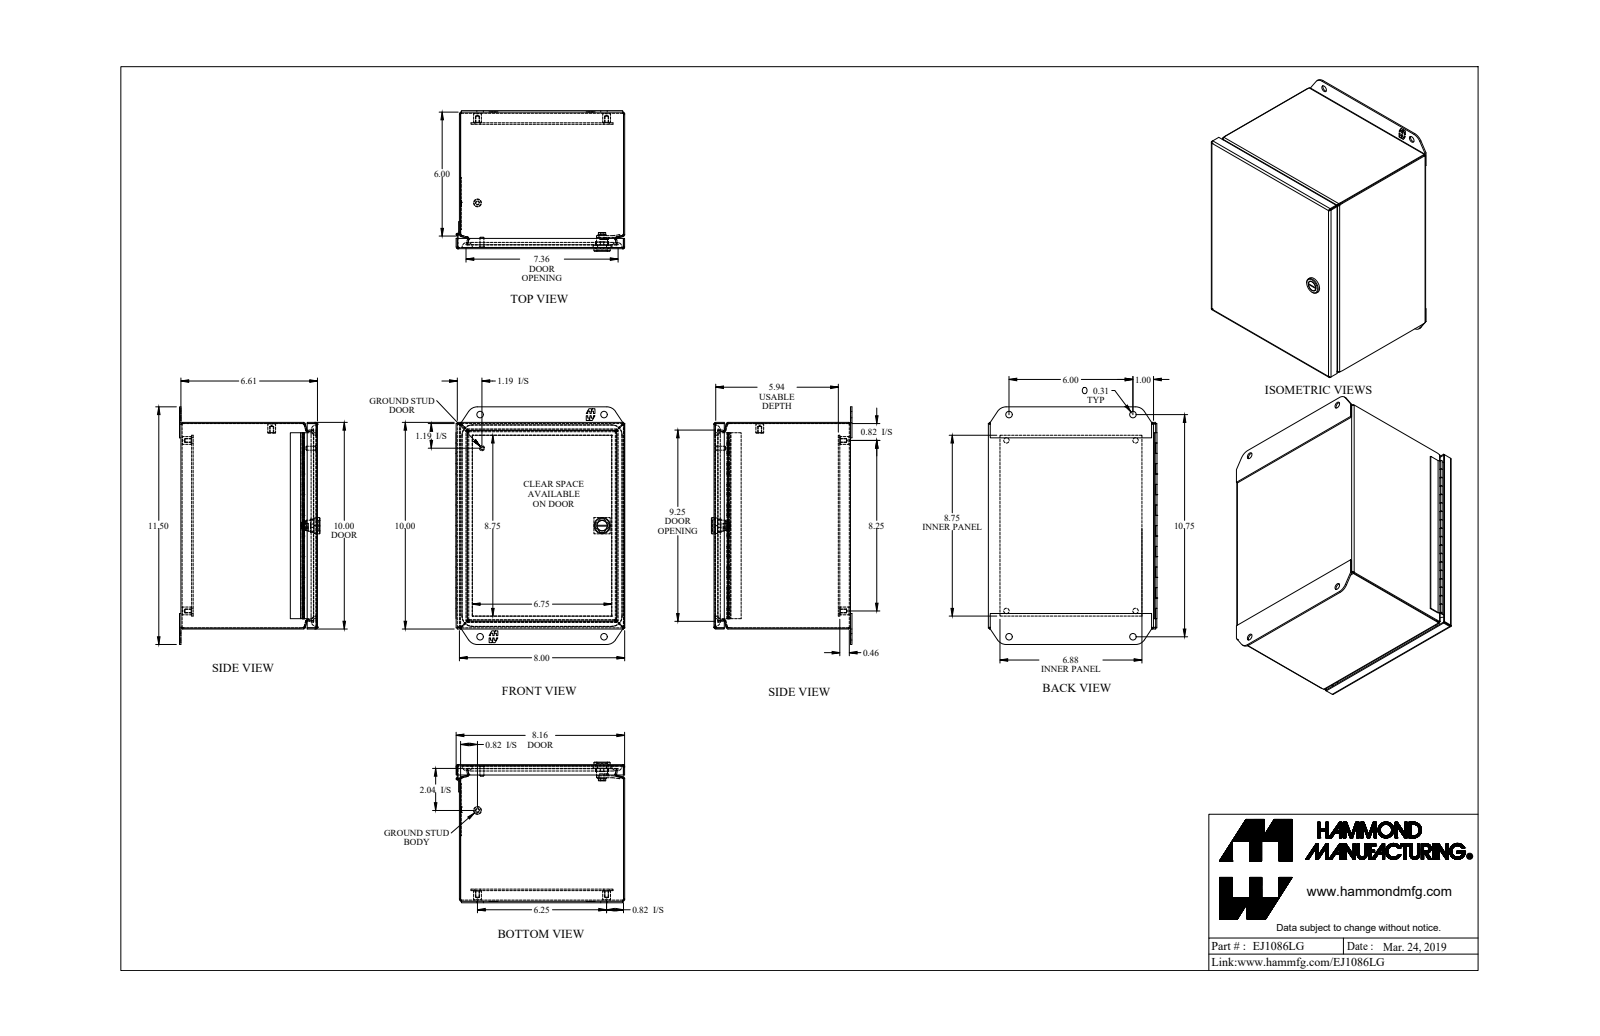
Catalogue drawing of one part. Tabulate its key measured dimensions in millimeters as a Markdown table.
| quantity | value |
| --- | --- |
| part name | EJ1086LG_Default |
| STEP written by | SolidWorks 2019 (CONFIG_CONTROL_DESIGN) |
| units | millimeters |
| bodies | 16 solids, 675 faces (377 planar, 206 cylindrical, 92 other) |
| overall size | 292.1 × 207.4 × 172.8 |
| volume | 548 300 mm³ |
| surface area | 716 100 mm² |
| round holes (diameter × count) | 4 × 5, 6.7 × 4, 8 × 4, 1.3 × 1, 13.1 × 1 |
| round bosses / shafts (diameter × count) | 9.5 × 5, 20 × 1, 13.6 × 1, 12.6 × 1, 11 × 1, 6.4 × 1, 4.8 × 1, 2.5 × 1 |
| partial cylindrical surfaces (radius × count) | 0.7 × 16, 2.2 × 16, 7.1 × 10, 6.4 × 4, 12.7 × 4, 12.7 × 4, 1.5 × 2, 13.7 × 2 |
| main face-to-face distances | 1.4, 166.5, 201.8, 252.6, 1.8, 15, 167.9, 165, 11.7, 13.1 |
| hole center spacings | 31.9, 31.9, 104.9, 152.4, 158.8, 158.8, 158.8, 185.6 |
